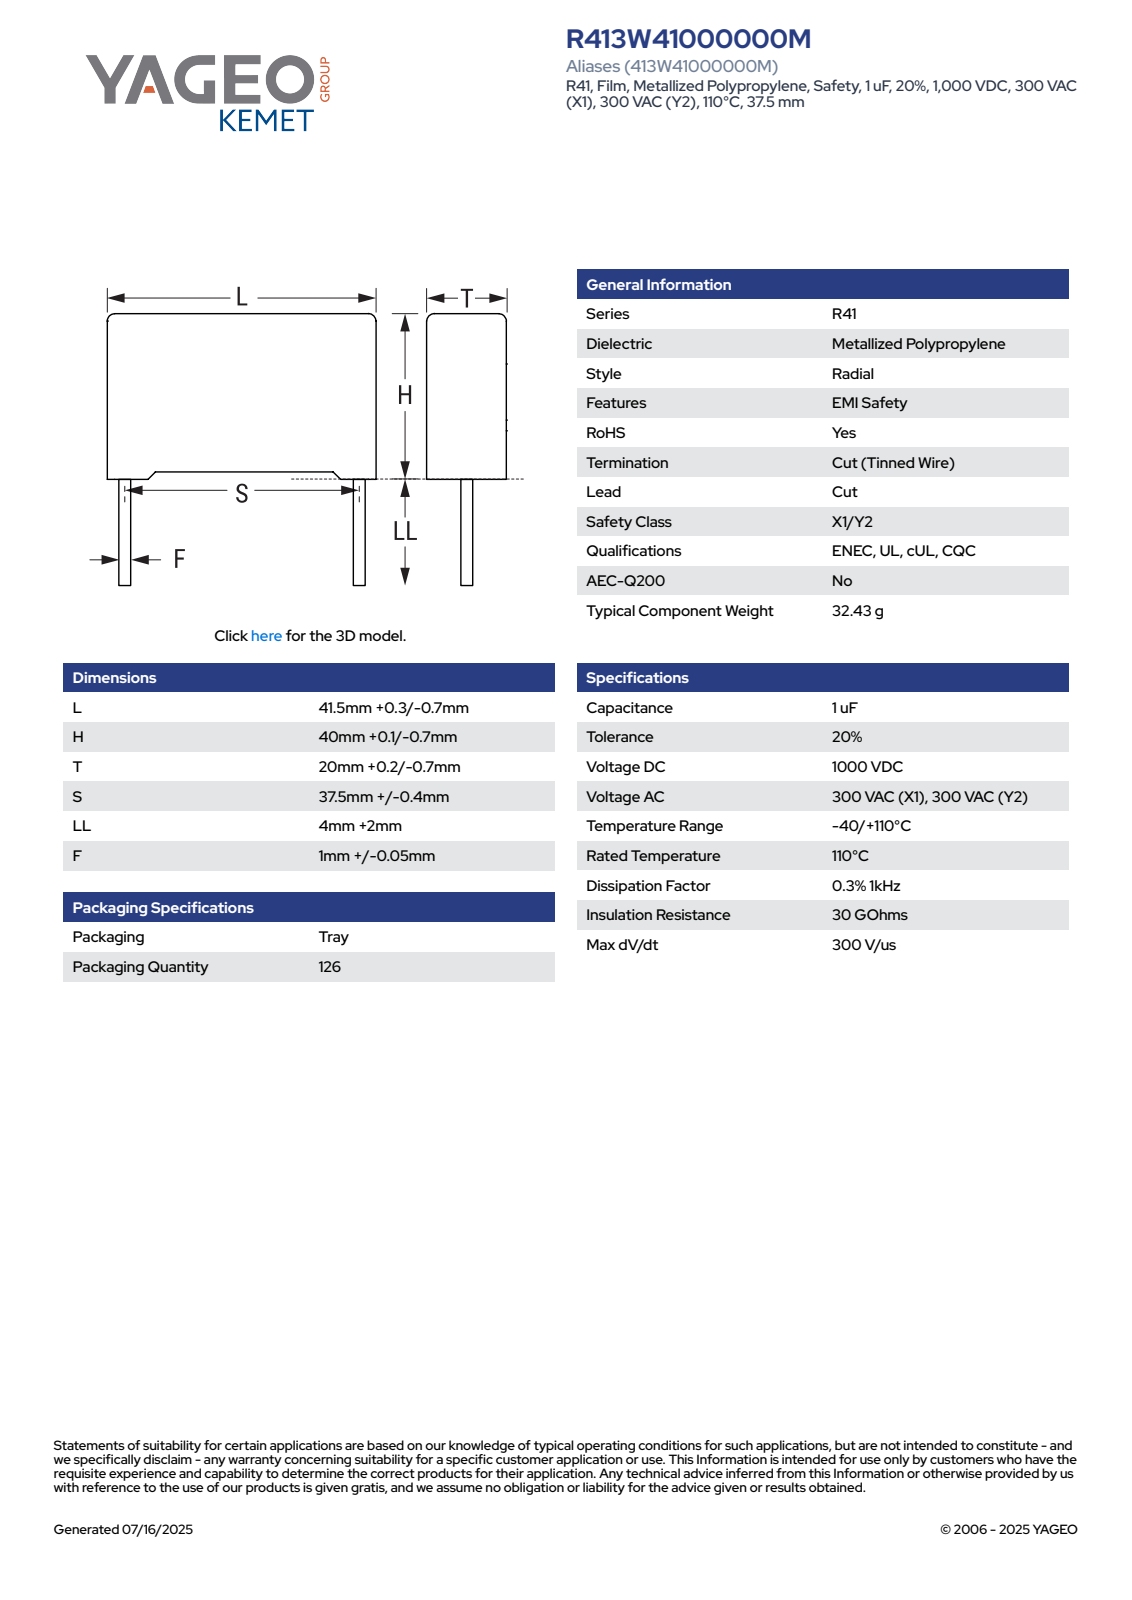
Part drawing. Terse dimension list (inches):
name: CFR_RB2_41.5X40X20_L41.8H40.1T20.2S37.5LL6F1.05
written by: SolidWorks 2021 (AUTOMOTIVE_DESIGN)
unit: in
bodies: 4 solids, 85 faces (77 planar, 8 cylindrical, 0 other)
size: 1.815 × 1.646 × 0.795
volume: 2.006 in³; area: 10.49 in²
bosses: 2× ⌀0.041
rounds: 4× R0.02
face distances: 0.795, 1.646, 1.524, 0.025, 1.549, 0.03, 0.054, 1.579, 0.055, 0.796
